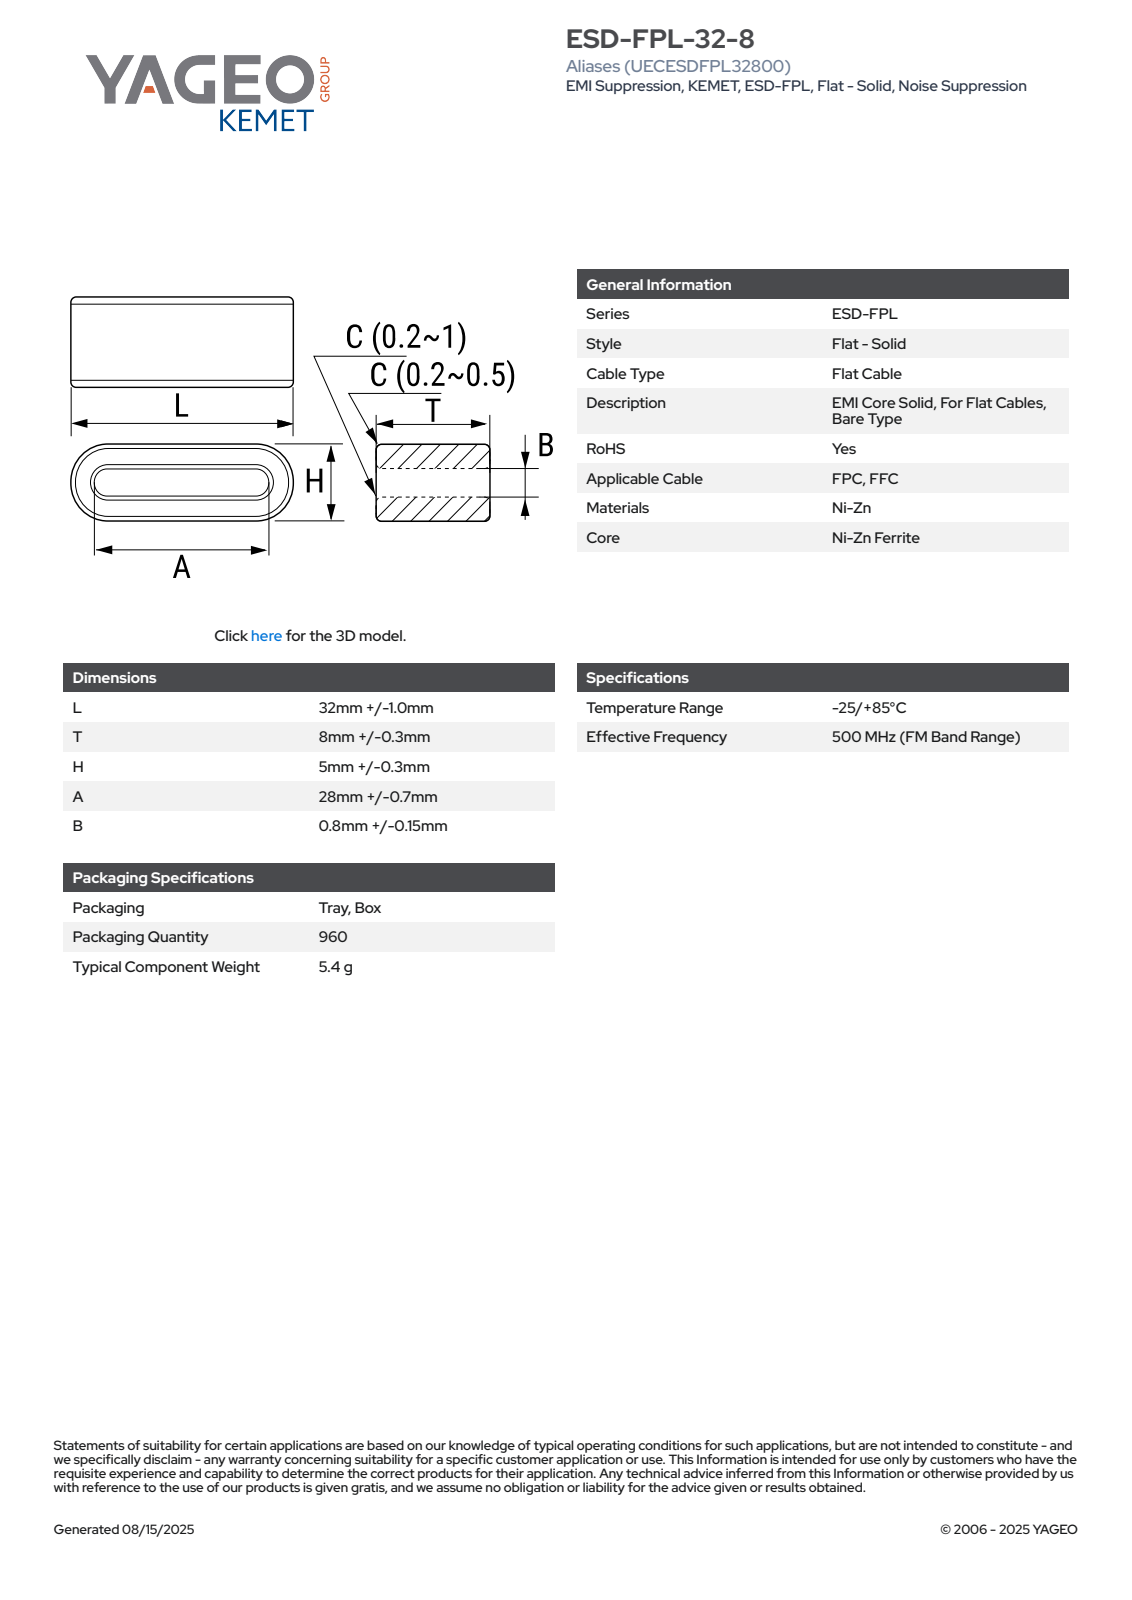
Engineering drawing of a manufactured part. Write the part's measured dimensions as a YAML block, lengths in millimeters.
part_name: "EC_FPL3_L33T8.3H5.3A28B0.8"
step_written_by: "SolidWorks 2021 (AUTOMOTIVE_DESIGN)"
units: millimeters
bodies: {solids: 4, faces: 95, planar: 63, cylindrical: 16, other: 16}
overall_size: [33, 8.3, 5.3]
volume: 1215
surface_area: 1366
partial_cylinders:
  - {radius: 0.2, count: 8}
  - {radius: 0.4, count: 2}
  - {radius: 2.65, count: 2}
face_to_face_distances: [2.25, 3.05, 5.3, 0.8, 8.3, 3.14, 5.16, 2.02, 0.5, 3.53]
